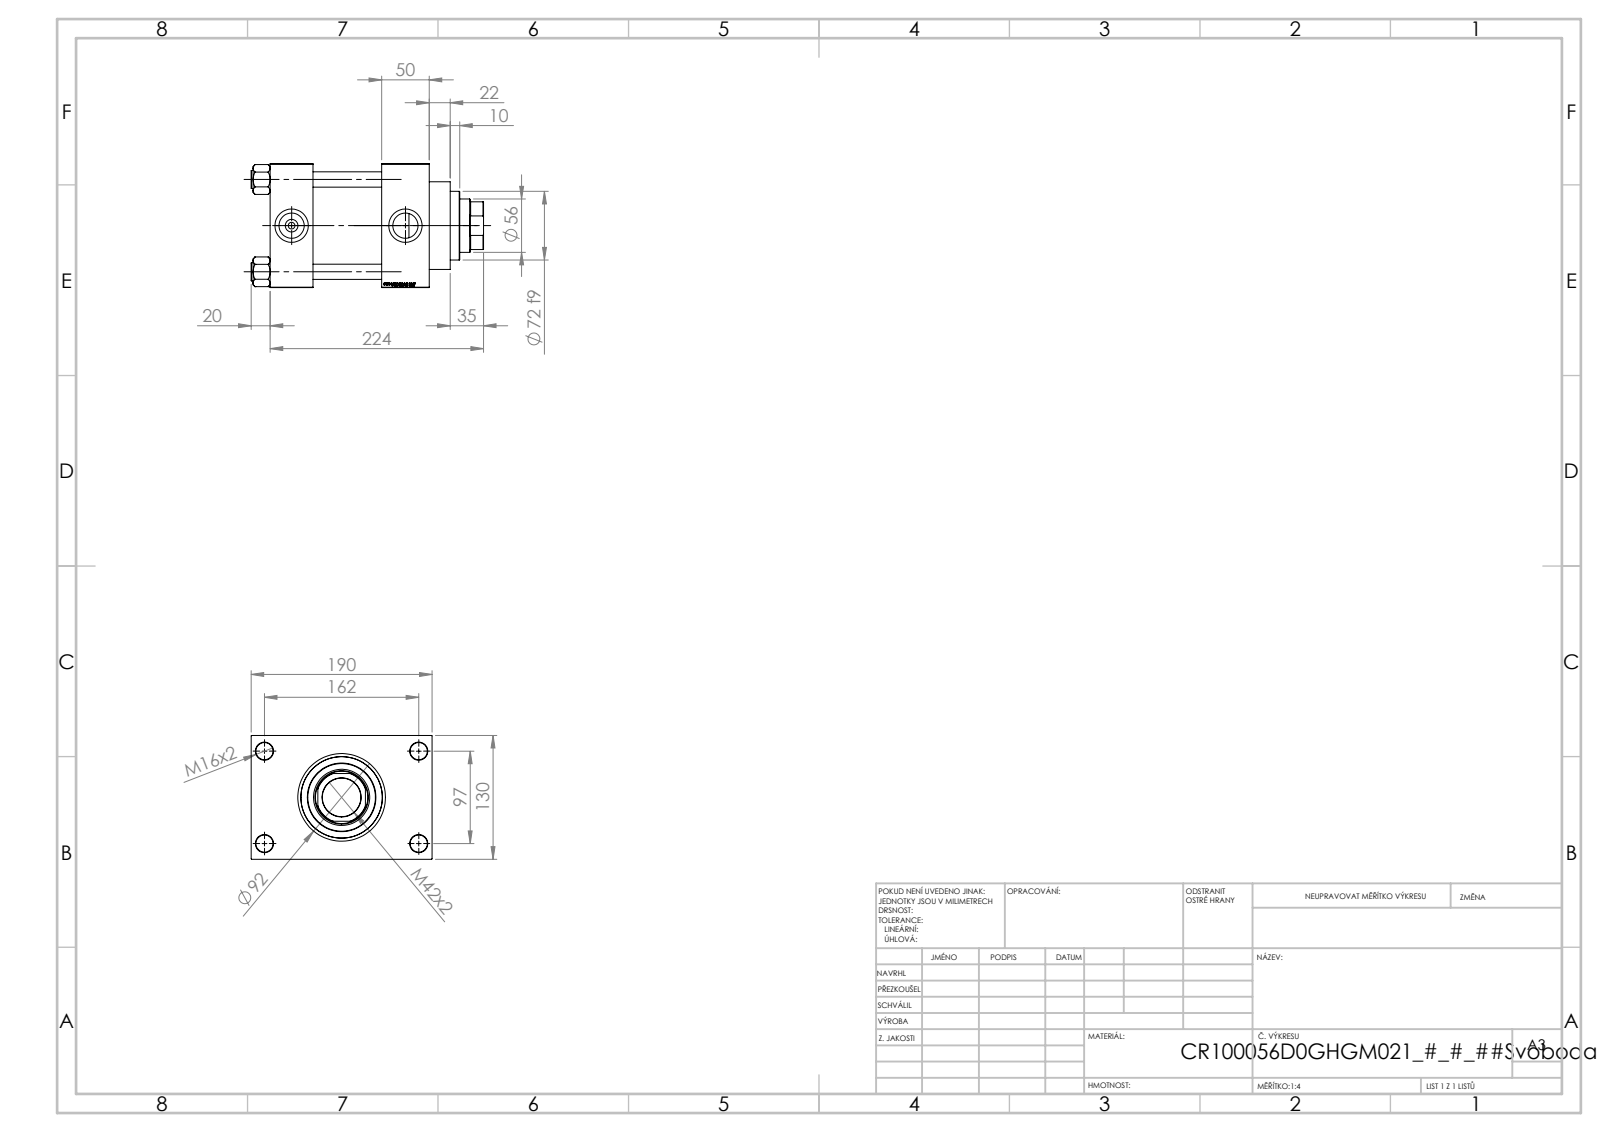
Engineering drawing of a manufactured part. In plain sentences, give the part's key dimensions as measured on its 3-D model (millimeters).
The part is named "V215CR_VCP_D; V215CR_D_TYCINKA; V215CR_D_Body; V215_VC_A (+1 more)". Its 3-D file was written by "SolidWorks 2019 (CONFIG_CONTROL_DESIGN)". It is 11 solids with 1151 faces: 545 planar, 88 cylindrical and 518 other. Overall it measures 244 by 190 by 130 millimeters. Its volume is 2 632 000 cubic millimeters and its surface area 363 387 square millimeters. Round holes: 4 of diameter 16, 4 of diameter 18, 2 of diameter 7, 2 of diameter 26.44, 2 of diameter 35, 1 of diameter 40.5, 1 of diameter 56, 1 of diameter 59, 1 of diameter 76, 1 of diameter 85.5, 1 of diameter 100. Round bosses or shafts: 4 of diameter 19, 1 of diameter 106, 1 of diameter 92, 1 of diameter 72. Partial cylindrical surfaces (rounded edges, fillets, slot ends): 1 of radius 27. The main face-to-face distances are 130, 72, 50, 45, 117, 167, 122, 30, 160, 21. The hole center spacings are 32.55, 68.52, 94.41, 96.9, 102.27, 129.45, 161.73, 97.
